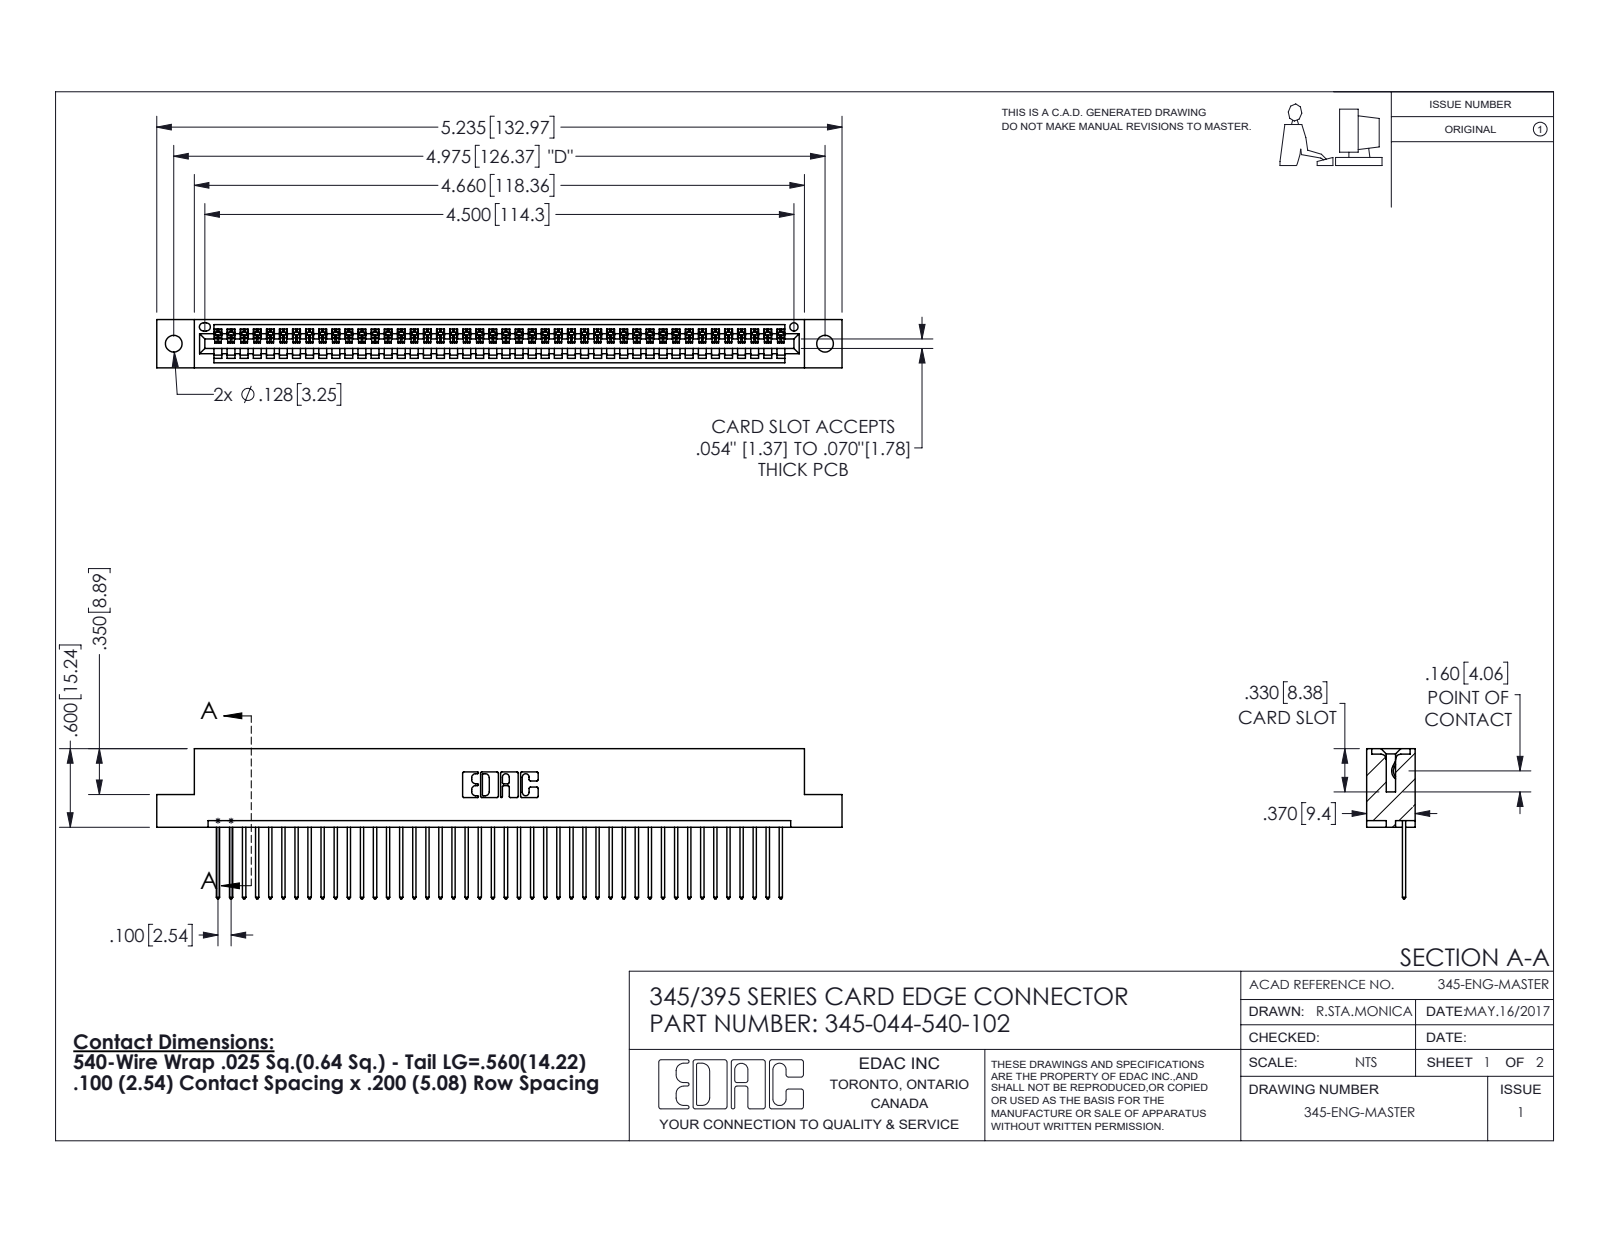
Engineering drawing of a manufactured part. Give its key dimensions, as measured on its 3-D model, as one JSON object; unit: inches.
{"part_name": "345-292-001_345-293-140; 345 Part_Flush Mounting Lugs - 0.128 Dia; 345-044-540-102", "step_written_by": "SolidWorks 2016 (CONFIG_CONTROL_DESIGN)", "units": "inches", "bodies": {"solids": 45, "faces": 2678, "planar": 1840, "cylindrical": 838, "other": 0}, "overall_size": [5.235, 1.147, 0.37], "volume_in3": 0.773, "surface_area_in2": 26.38, "round_holes": [[0.128, 2], [0.064, 1]], "partial_cylinders_radius": [[0.006, 88], [0.01, 88], [0.01, 22], [0.007, 6], [0.031, 6], [0.026, 3], [0.031, 2], [0.04, 2]], "face_to_face_distances": [0.298, 0.072, 0.37, 0.2, 0.098, 0.272, 0.025, 0.225, 0.149, 0.072], "hole_center_spacings": [0.27, 4.739, 4.975]}
